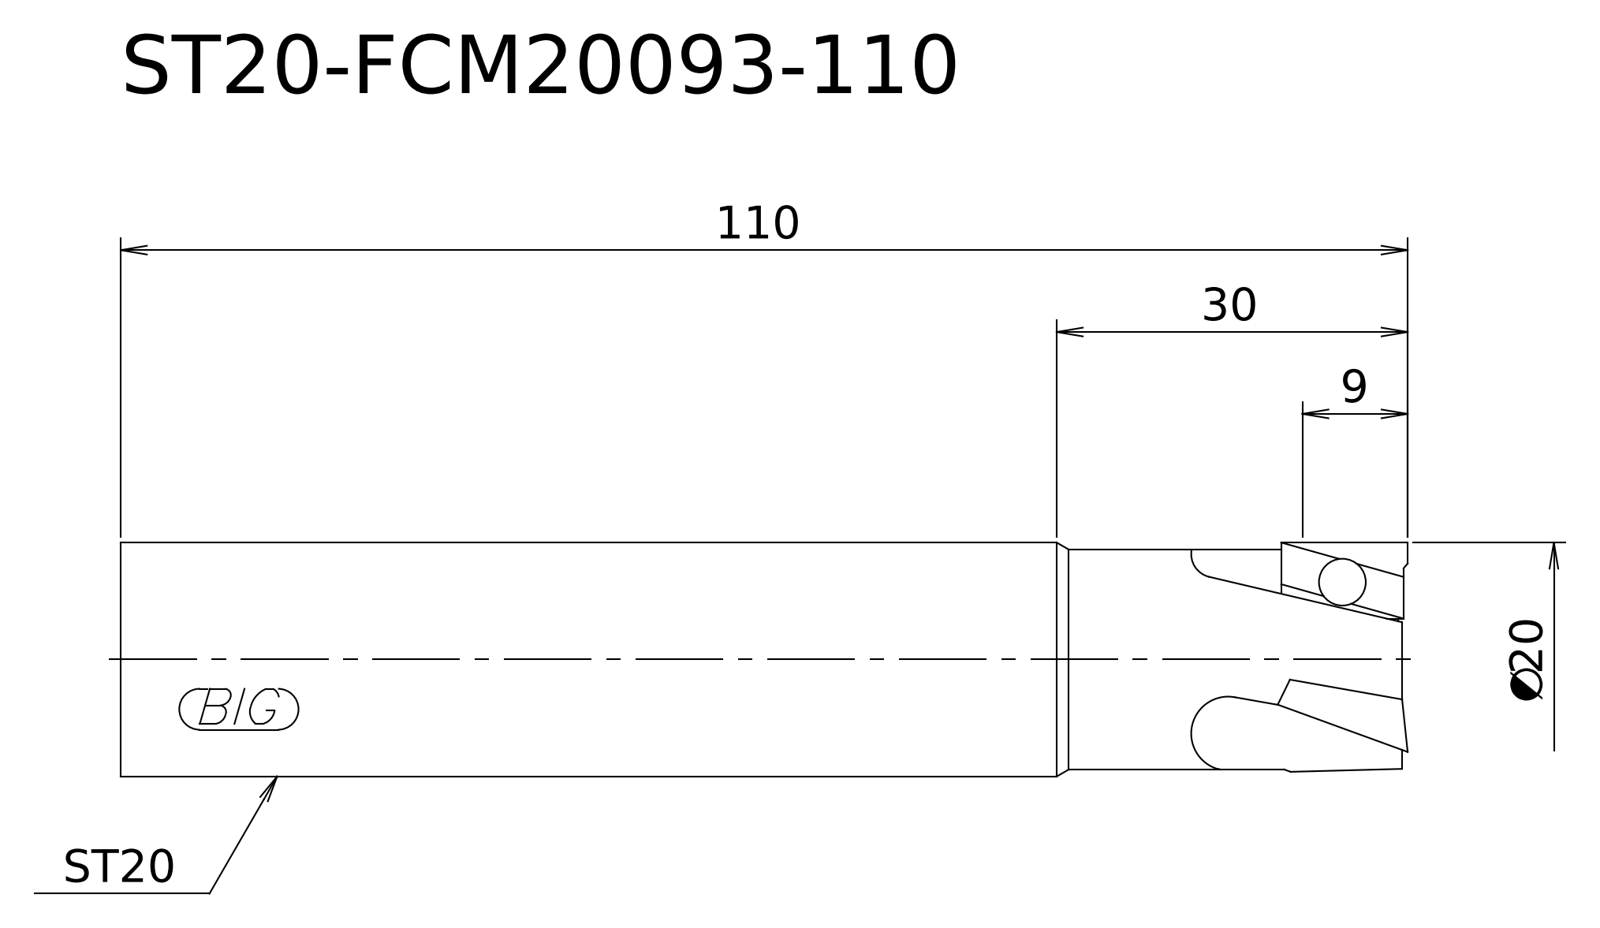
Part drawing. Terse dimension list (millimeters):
written by: Kubotek KeyCreator V8.5.1 (14335) (CONFIG_CONTROL_DESIGN)
unit: mm
bodies: 1 solid, 7 faces (3 planar, 3 cylindrical, 1 other)
size: 110 × 20 × 20
volume: 33 875 mm³; area: 7 516 mm²
bosses: 1× ⌀20, 1× ⌀18.8
face distances: 110, 10.81, 99.19
